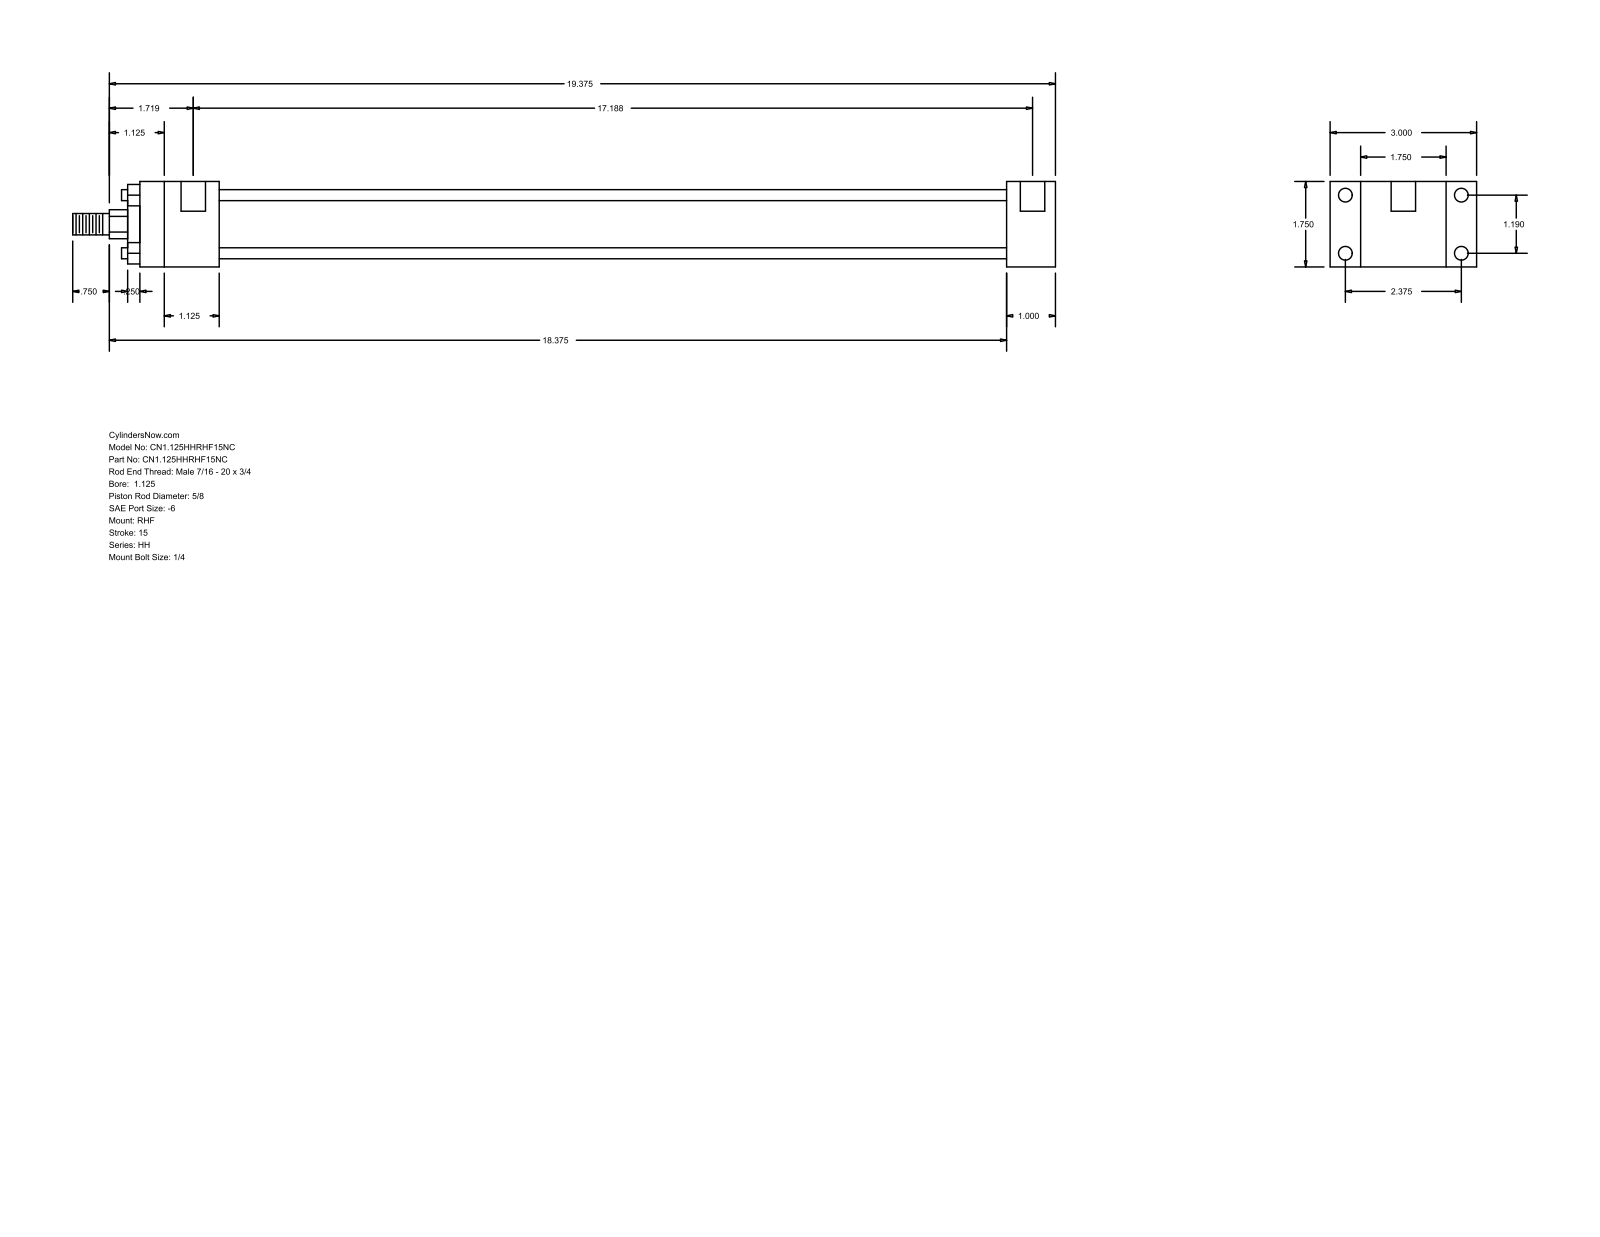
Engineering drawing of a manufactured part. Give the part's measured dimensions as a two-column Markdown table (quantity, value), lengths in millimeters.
| quantity | value |
| --- | --- |
| part name | HH_RHF__0112_0.625 |
| STEP written by | GSSL Pune (CONFIG_CONTROL_DESIGN) |
| units | millimeters |
| bodies | 0 solids, 88 faces (60 planar, 28 cylindrical, 0 other) |
| overall size | 511.18 × 76.2 × 44.45 |
| round holes (diameter × count) | 5.56 × 4, 7.14 × 4, 12.7 × 2 |
| round bosses / shafts (diameter × count) | 5.71 × 4, 34.92 × 1, 28.57 × 1, 15.88 × 1, 11.11 × 1 |
| partial cylindrical surfaces (radius × count) | 7.54 × 1 |
| main face-to-face distances | 44.46, 15.87, 60.33, 25.39, 76.2, 409.58, 434.97, 41.27, 450.85, 476.24 |
| hole center spacings | 30.22, 60.32, 67.47, 433.39, 3.17, 436.56 |
